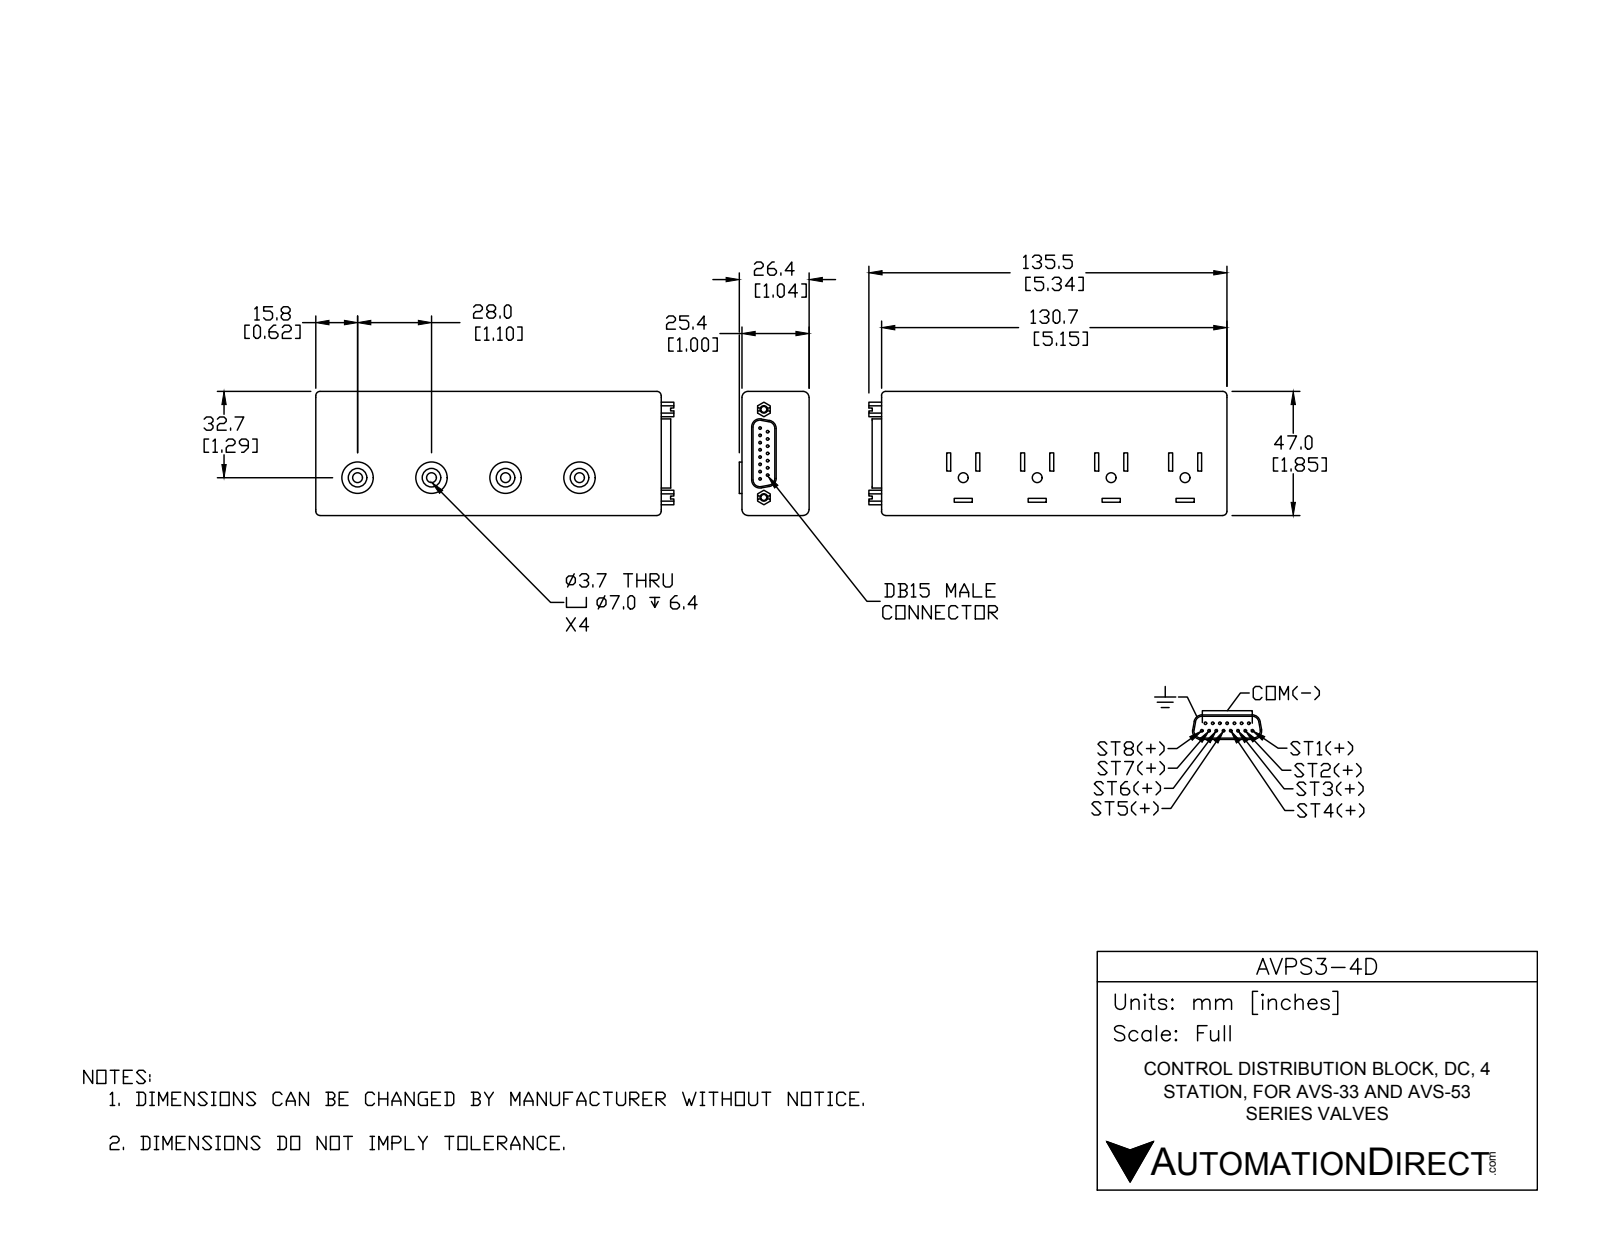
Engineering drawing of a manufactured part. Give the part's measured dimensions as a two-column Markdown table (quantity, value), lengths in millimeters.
| quantity | value |
| --- | --- |
| part name | AVPS3-4D |
| STEP written by | SolidWorks 2016 (AUTOMOTIVE_DESIGN) |
| units | millimeters |
| bodies | 1 solid, 219 faces (127 planar, 80 cylindrical, 12 other) |
| overall size | 135.5 × 47 × 26.4 |
| volume | 152 800 mm³ |
| surface area | 24 550 mm² |
| round holes (diameter × count) | 3.7 × 4, 7 × 4, 2.3 × 2 |
| round bosses / shafts (diameter × count) | 1 × 15, 11.9 × 4 |
| partial cylindrical surfaces (radius × count) | 1.6 × 8, 2.3 × 4, 2.6 × 4, 3.1 × 4 |
| main face-to-face distances | 25.4, 47, 130.7, 28, 1.5, 56, 11, 1, 26.4, 29.5 |
| hole center spacings | 28, 56, 33.3, 84 |
